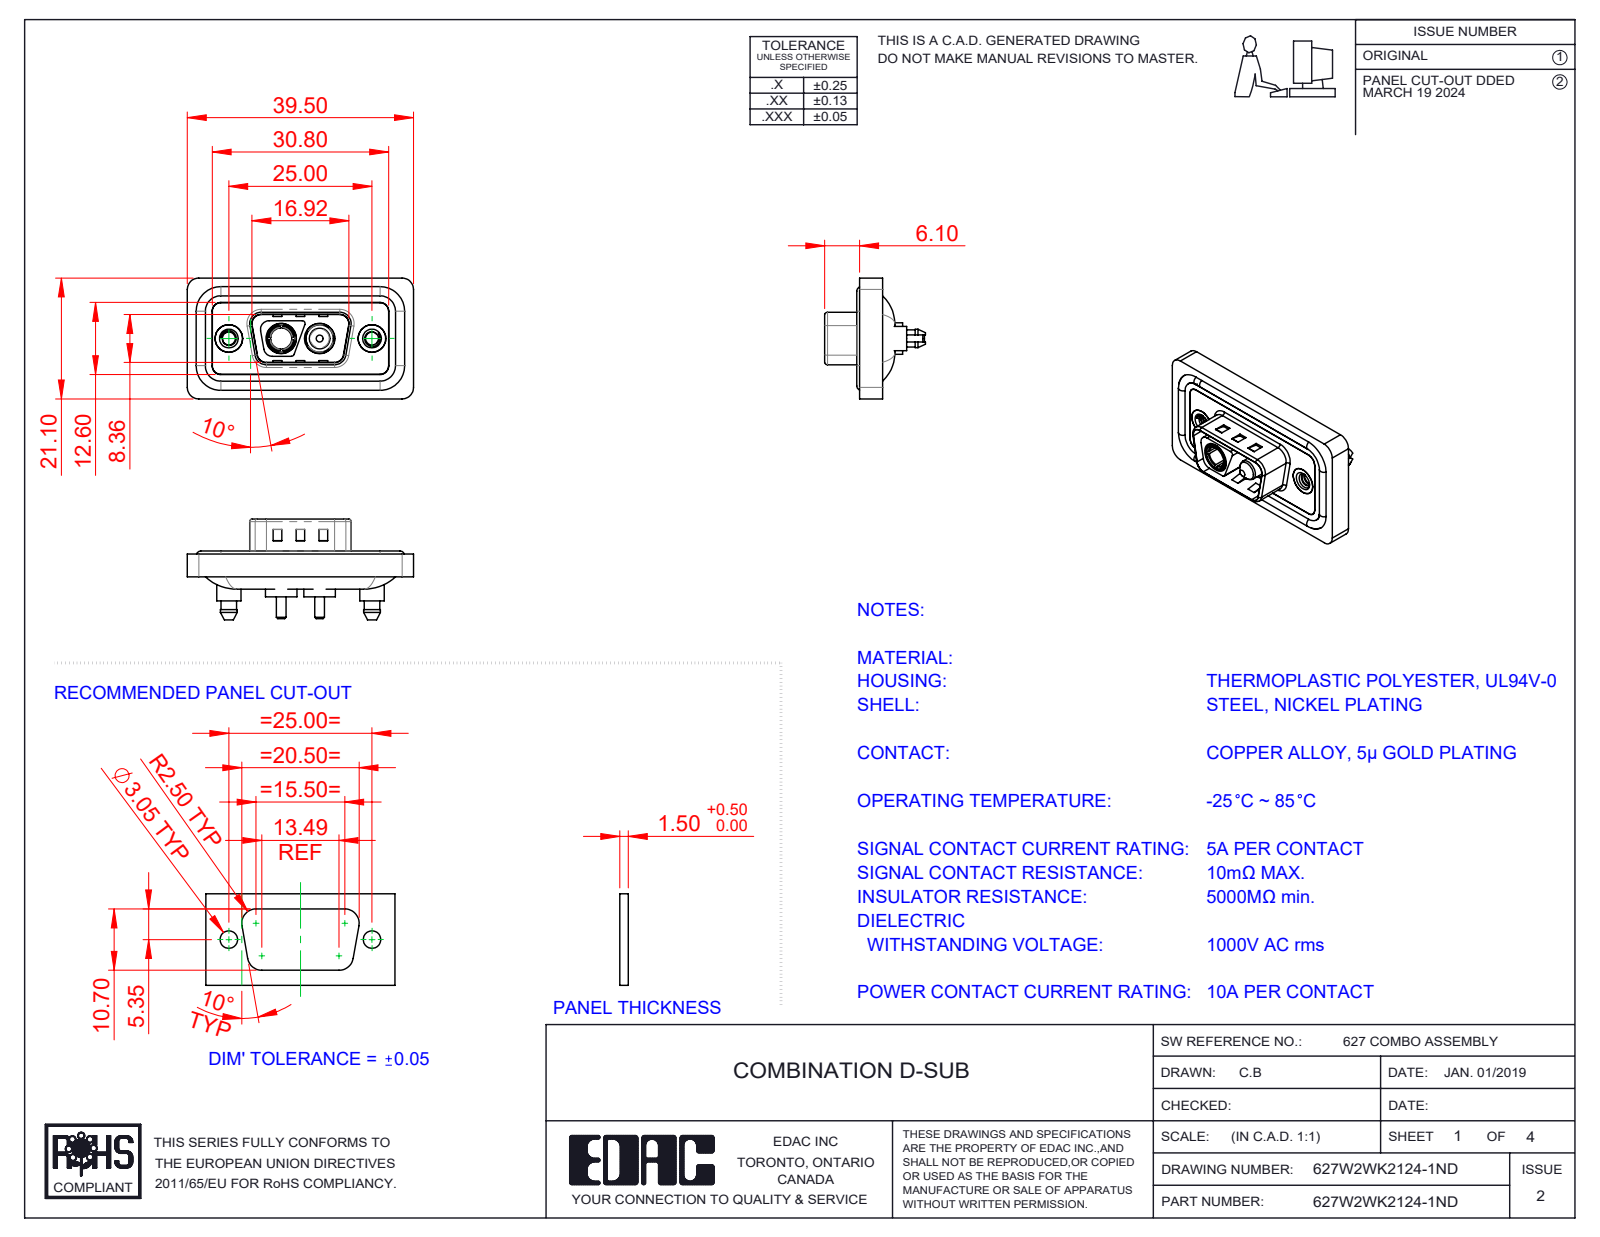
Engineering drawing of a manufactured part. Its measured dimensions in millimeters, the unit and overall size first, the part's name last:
Units: millimetres
Overall size (bounding box): 39.5 × 21.1 × 17.6
Round holes (diameter × count): ⌀2.26 ×2, ⌀4 ×2, ⌀4.8 ×2, ⌀4.85 ×2, ⌀5 ×2, ⌀5.3 ×2, ⌀3.7 ×1
Round bosses / shafts (diameter × count): ⌀1.6 ×4, ⌀5.5 ×2, ⌀5.4 ×2, ⌀5.2 ×2, ⌀4.9 ×2, ⌀4.75 ×2, ⌀4.25 ×2, ⌀3.75 ×2
Partial cylindrical surfaces — rounded edges, fillets, slot ends (radius × count): R1.5 ×26, R2 ×18, R0.5 ×10, R1.6 ×10, R0.25 ×4, R0.6 ×4, R0.65 ×4, R0.9 ×4
Main face-to-face distances: 0.4, 1.1, 2.9, 0.5, 1.6, 3.1, 1.5, 4, 1.8, 3.2
Hole centre spacings: 9.14, 15.86, 6.72, 25
Volume: 4 659 mm³ · Surface area: 7 653 mm²
Bodies: 11 solids, 592 faces (205 planar, 267 cylindrical, 120 other)
Part name (STEP PRODUCT): Power Pin_10A S; 627Combo Shell Front_09 Contacts; 627Combo Shell Rear_09 Contacts; 627Combo Threaded Boardlock_5 (+5 more)
STEP written by: SolidWorks 2023 (CONFIG_CONTROL_DESIGN)
